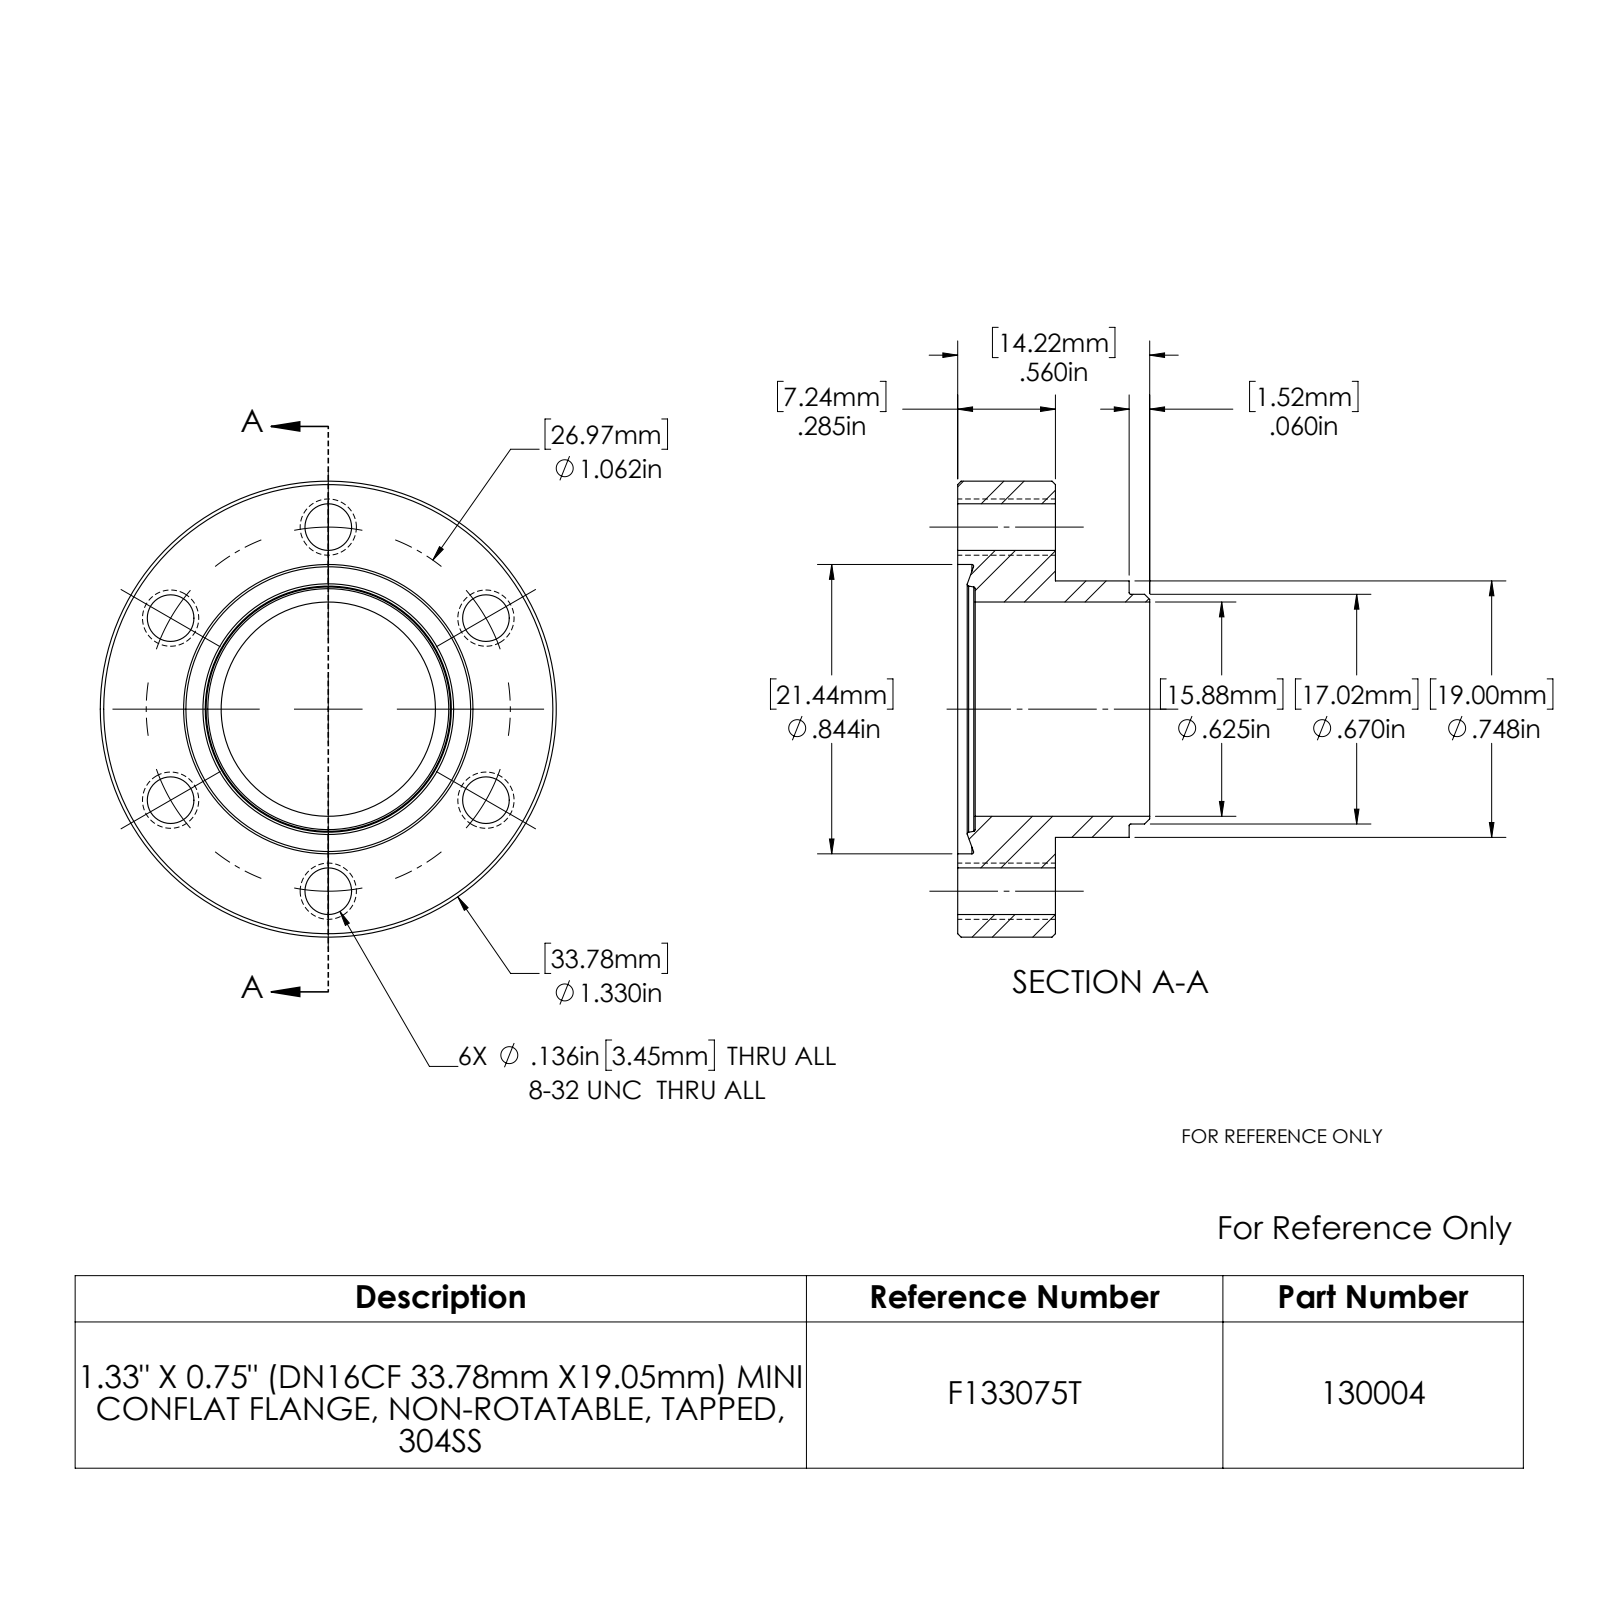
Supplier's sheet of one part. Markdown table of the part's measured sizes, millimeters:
| quantity | value |
| --- | --- |
| part name | 130004 |
| STEP written by | SolidWorks 2022 (AUTOMOTIVE_DESIGN) |
| units | millimeters |
| bodies | 1 solid, 45 faces (5 planar, 22 cylindrical, 18 other) |
| overall size | 33.8 × 33.8 × 14.2 |
| volume | 4 980 mm³ |
| surface area | 3 634 mm² |
| round holes (diameter × count) | 3.5 × 6, 15.9 × 1, 21.4 × 1 |
| round bosses / shafts (diameter × count) | 33.8 × 1, 19 × 1, 17 × 1 |
| main face-to-face distances | 7.2, 1.3, 5.9, 12.7, 11.4, 5.5, 14.2, 12.9, 7, 1.5 |
| hole center spacings | 13.5, 23.4, 13.5, 27, 27 |
